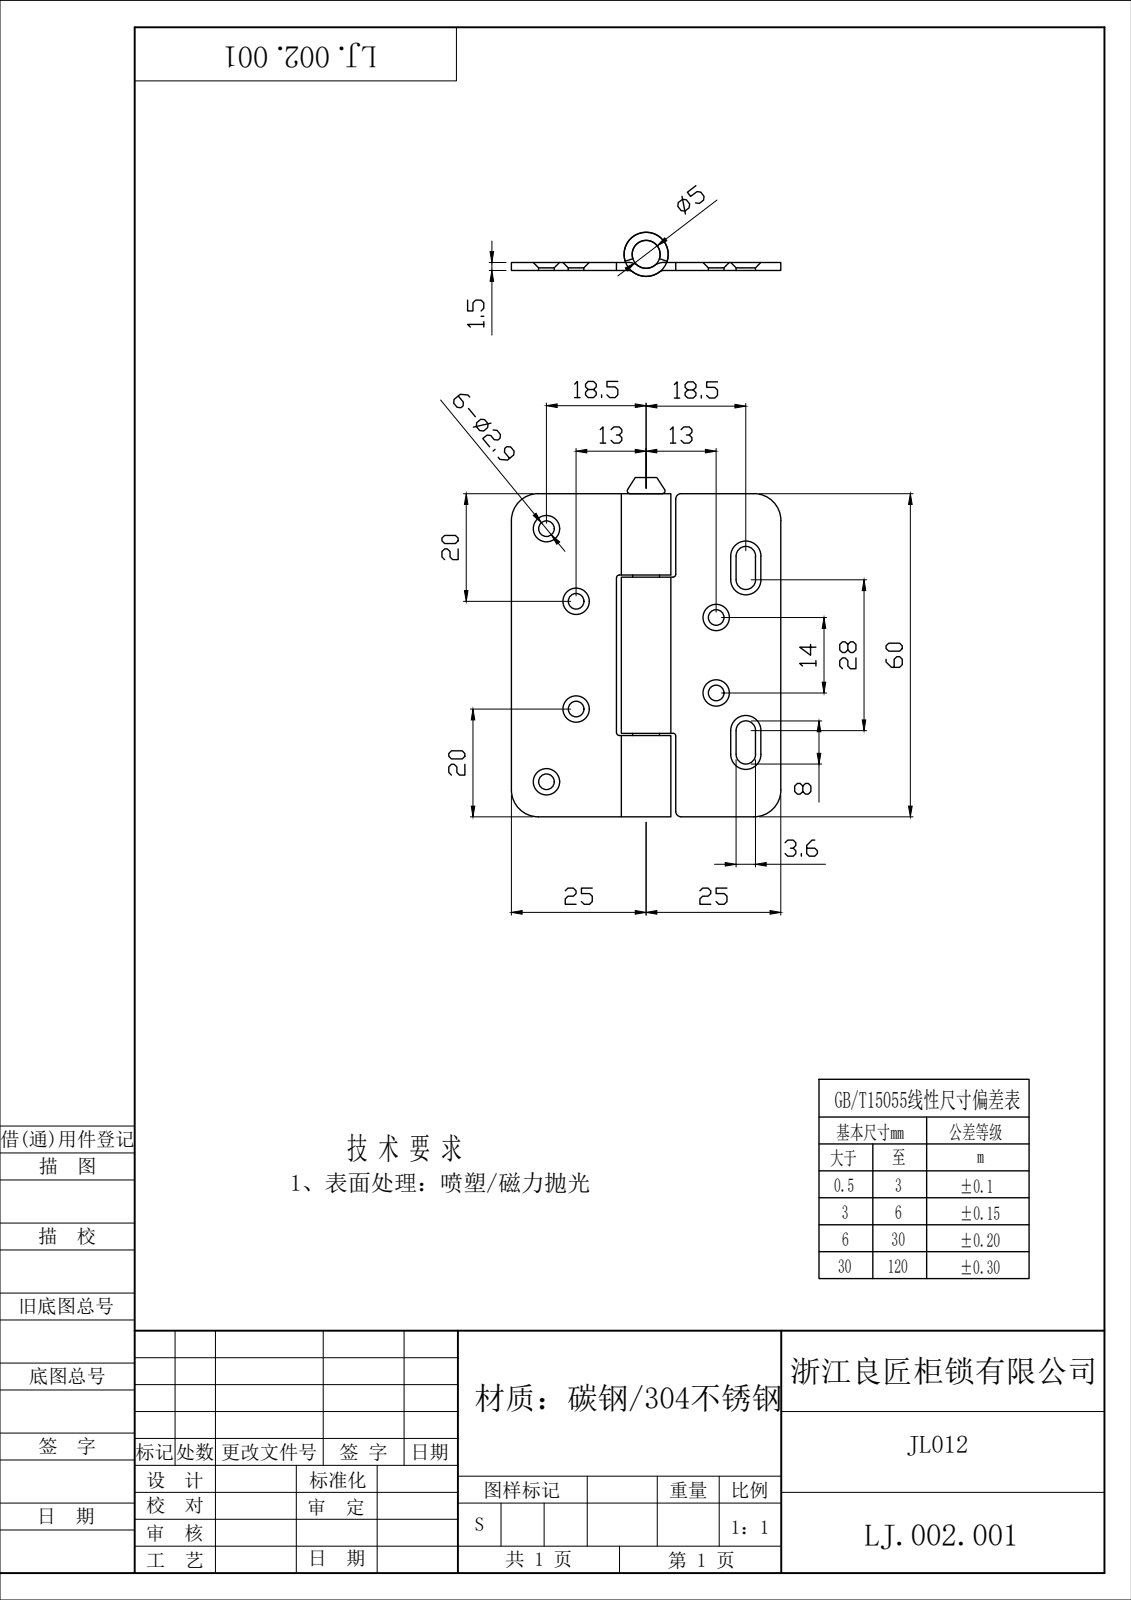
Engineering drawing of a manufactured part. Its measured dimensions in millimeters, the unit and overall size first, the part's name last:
Units: millimetres
Overall size (bounding box): 63 × 50 × 8.2
Round holes (diameter × count): ⌀2.9 ×6, ⌀5.2 ×1
Round bosses / shafts (diameter × count): ⌀8.2 ×1, ⌀5 ×1
Partial cylindrical surfaces — rounded edges, fillets, slot ends (radius × count): R0.5 ×4, R1.8 ×4, R5 ×4, R1 ×2, R1.5 ×2, R3 ×2
Main face-to-face distances: 1.5, 19.5, 30.5, 60, 50, 15.1, 44.9, 15.5, 44.5, 0.4
Hole centre spacings: 14, 17.39, 26, 29.53, 30.99, 35.56, 43.85, 47
Volume: 6 508 mm³ · Surface area: 8 908 mm²
Bodies: 3 solids, 95 faces (35 planar, 40 cylindrical, 20 other)
STEP written by: Rhino 8.5 (CONFIG_CONTROL_DESIGN)
